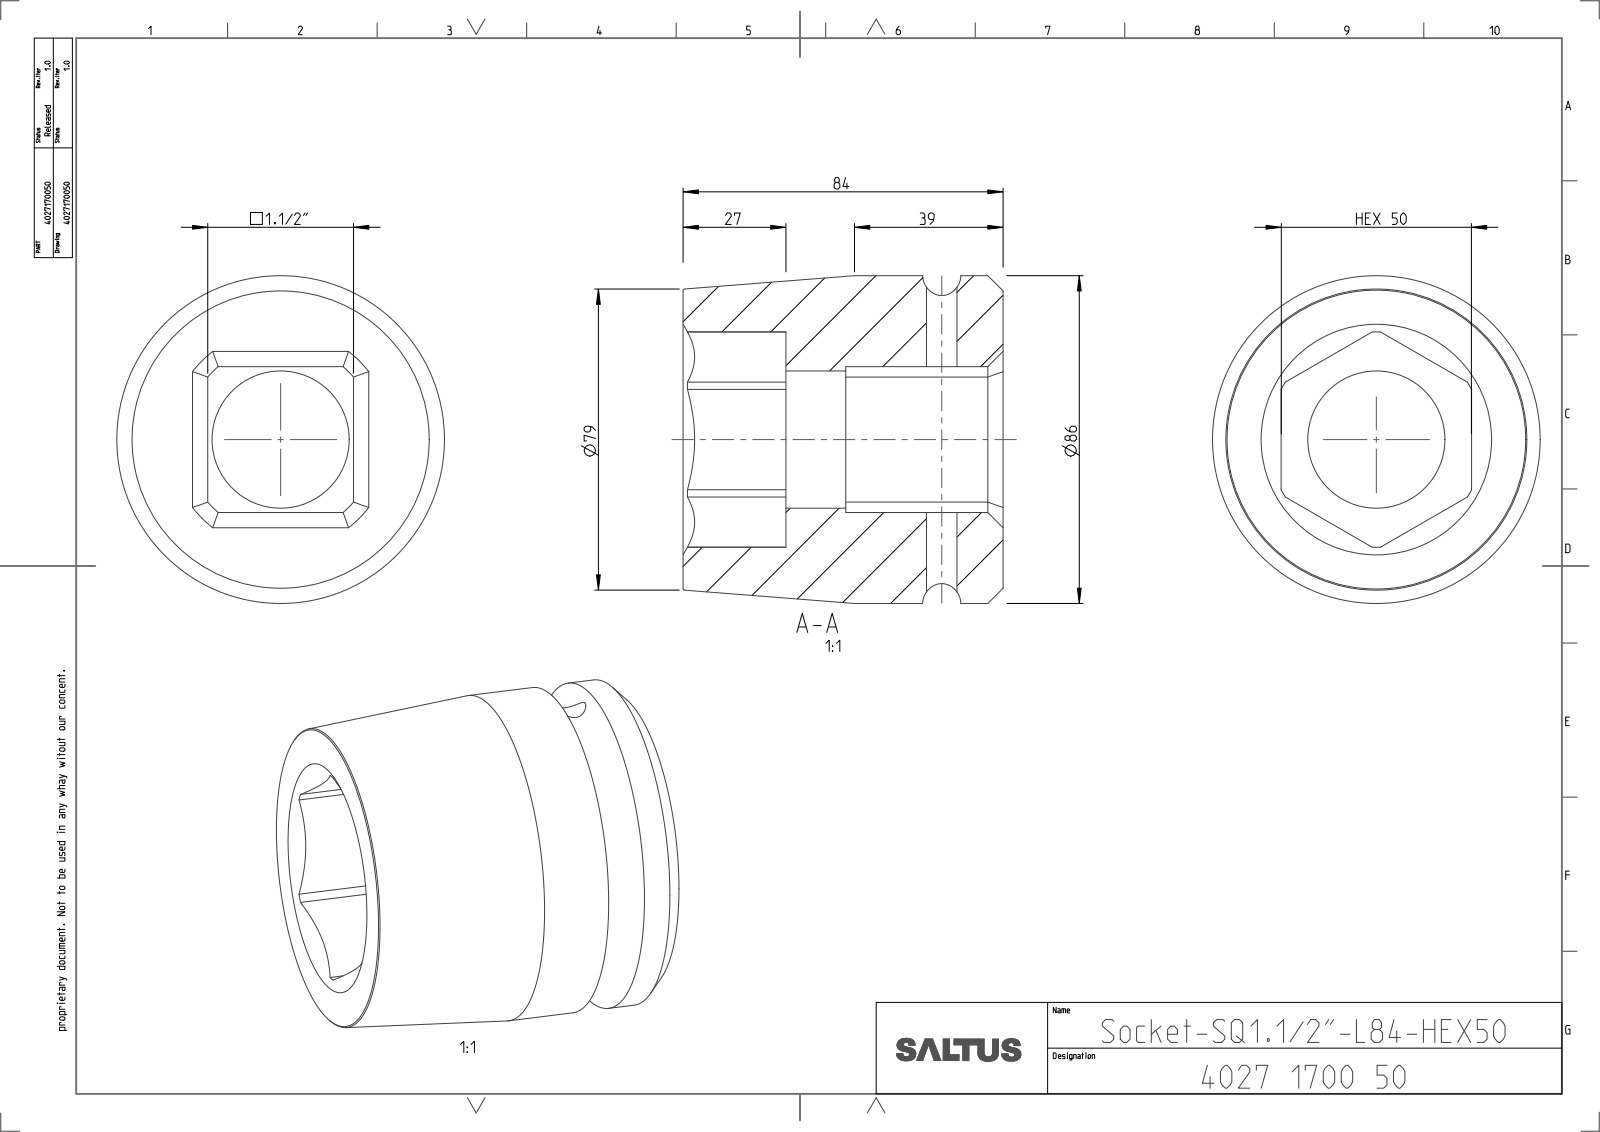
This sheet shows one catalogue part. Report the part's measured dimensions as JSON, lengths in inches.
{"part_name": "4027170050", "step_written_by": "CREO PARAMETRIC BY PTC INC, 2022414 (CONFIG_CONTROL_DESIGN)", "units": "inches", "bodies": {"solids": 1, "faces": 52, "planar": 18, "cylindrical": 20, "other": 14}, "overall_size": [3.386, 3.386, 3.307], "volume_in3": 19.32, "surface_area_in2": 68.3, "round_holes": [[0.315, 1], [1.417, 1]], "round_bosses_or_shafts": [[3.386, 1]], "partial_cylinders_radius": [[0.992, 1], [1.112, 1]], "face_to_face_distances": [1.507, 3.307, 1.969, 0.231, 1.738, 2.244, 1.063, 1.626, 0.618, 1.681]}
